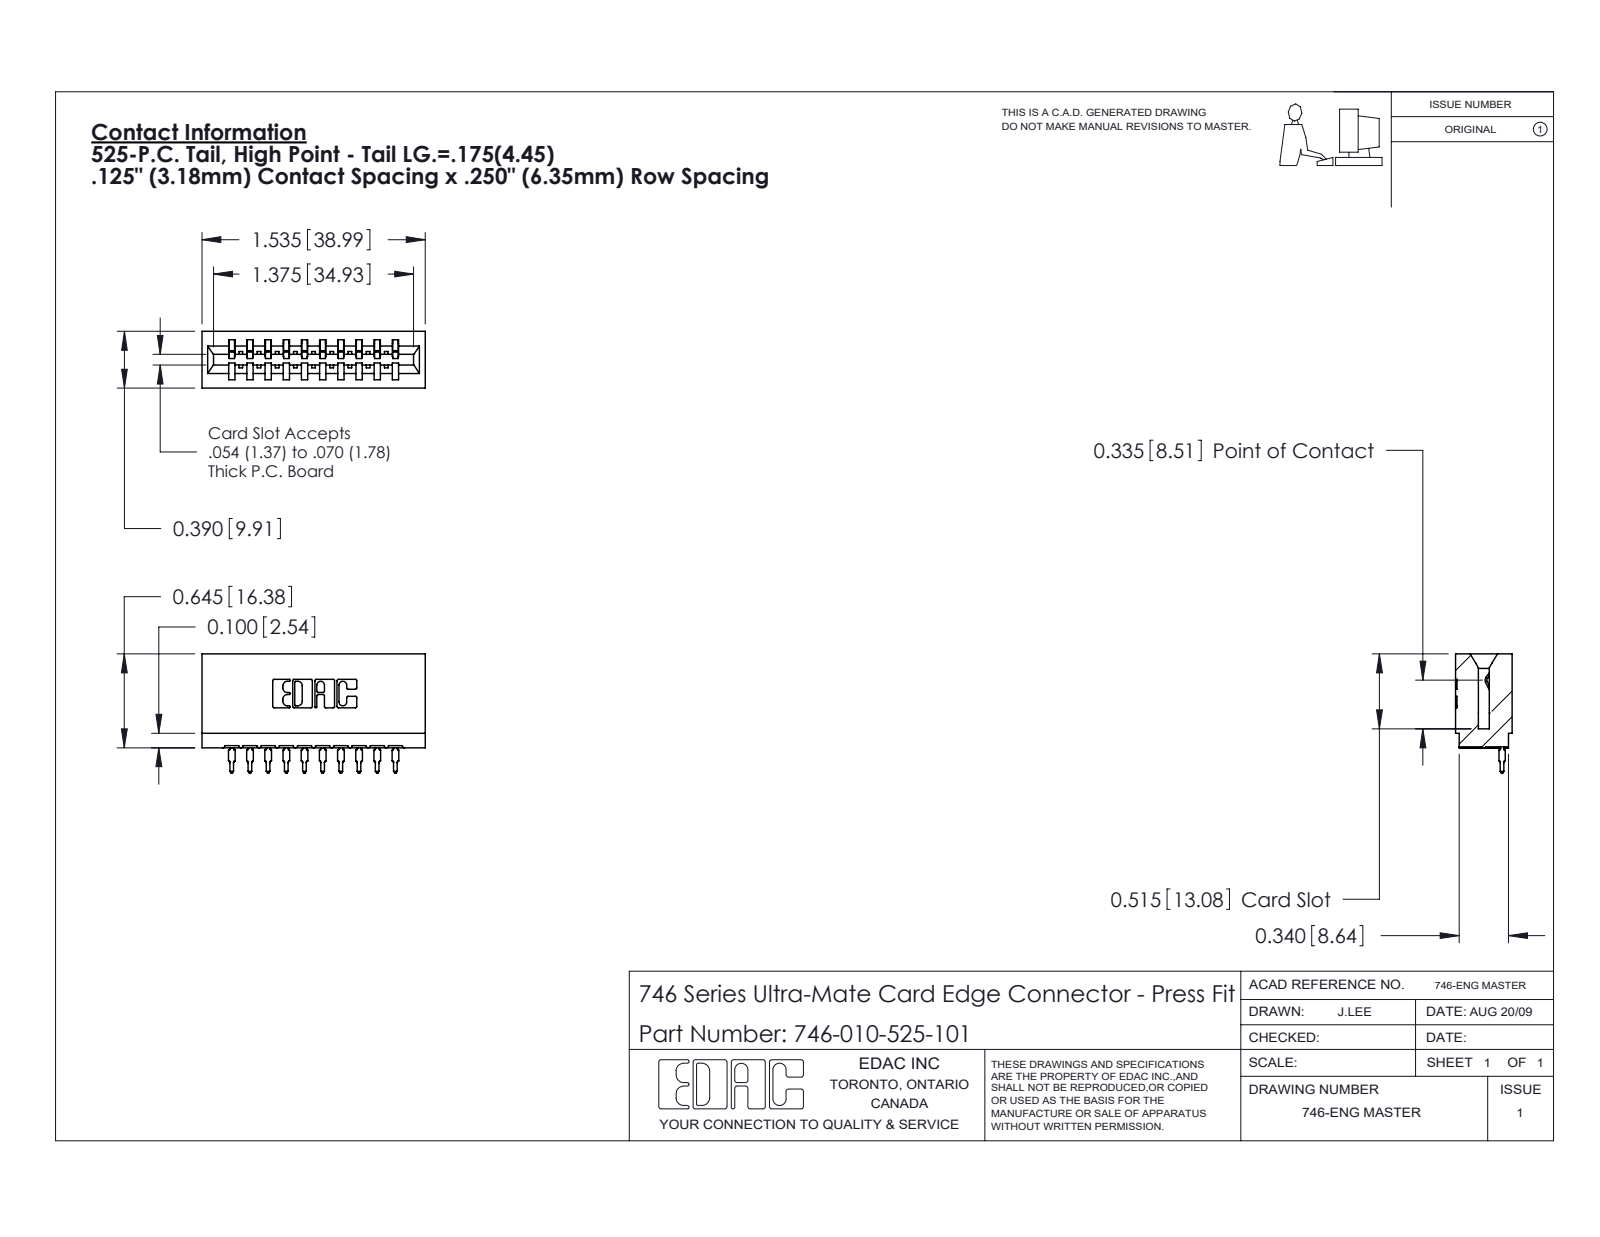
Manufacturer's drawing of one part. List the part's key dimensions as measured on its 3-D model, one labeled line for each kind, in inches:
Part name (STEP PRODUCT): 746 Part_.515 Slot Depth - 01; 746-292-001_525; 746-010-525-101
STEP written by: SolidWorks 2020 (CONFIG_CONTROL_DESIGN)
Units: inches
Bodies: 11 solids, 1177 faces (685 planar, 232 cylindrical, 260 other)
Overall size (bounding box): 1.535 × 0.819 × 0.39
Volume: 0.261 in³ · Surface area: 8.924 in²
Partial cylindrical surfaces — rounded edges, fillets, slot ends (radius × count): R0.01 ×22, R0.021 ×20, R0.015 ×11, R0.007 ×6, R0.031 ×6, R0.005 ×4, R0.011 ×4, R0.026 ×3
Main face-to-face distances: 0.25, 0.5, 0.333, 0.125, 0.042, 0.057, 0.375, 0.208, 0.125, 0.39
